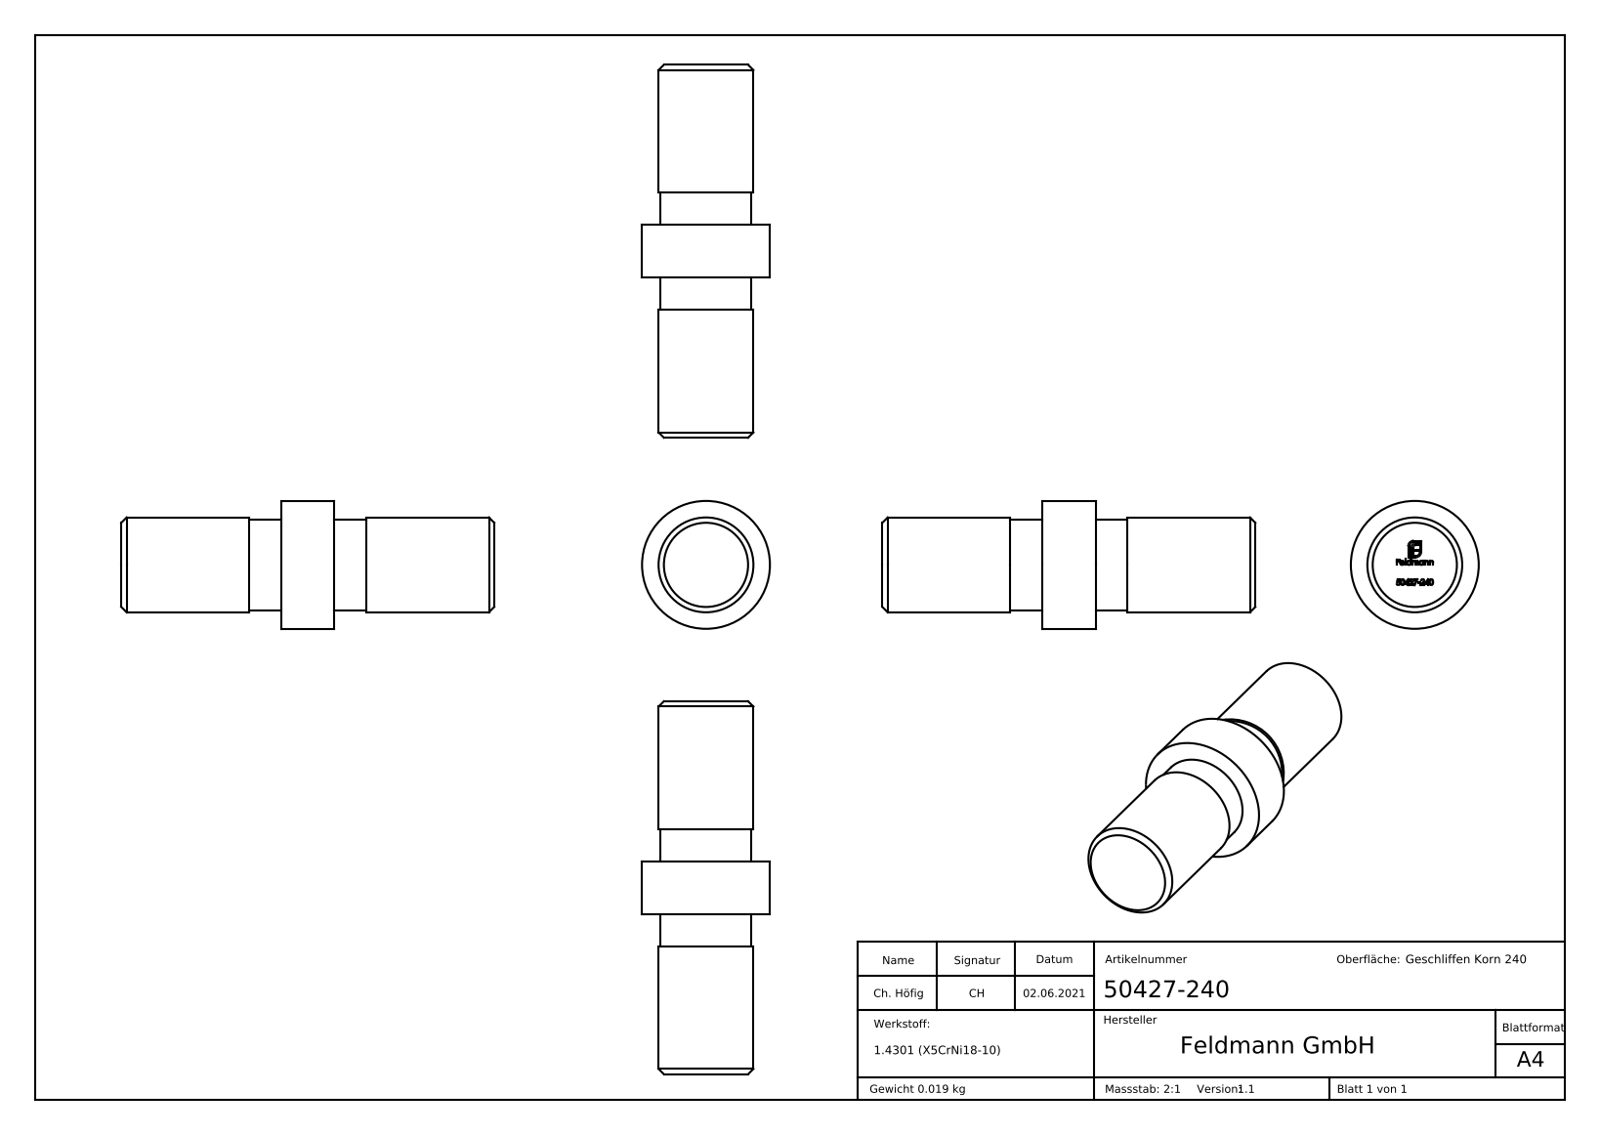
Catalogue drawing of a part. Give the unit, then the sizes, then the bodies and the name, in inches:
Units: inches
Overall size (bounding box): 1.378 × 0.472 × 0.472
Round bosses / shafts (diameter × count): ⌀0.472 ×1, ⌀0.35 ×1, ⌀0.335 ×1
Main face-to-face distances: 0.591, 0.787, 0.197, 1.378, 0.472, 0.906, 0.118, 0.315, 0.433, 0.469
Volume: 0.146 in³ · Surface area: 1.947 in²
Bodies: 1 solid, 281 faces (161 planar, 10 cylindrical, 110 other)
Part name (STEP PRODUCT): 50427-240
STEP written by: SolidWorks 2018 (CONFIG_CONTROL_DESIGN)
